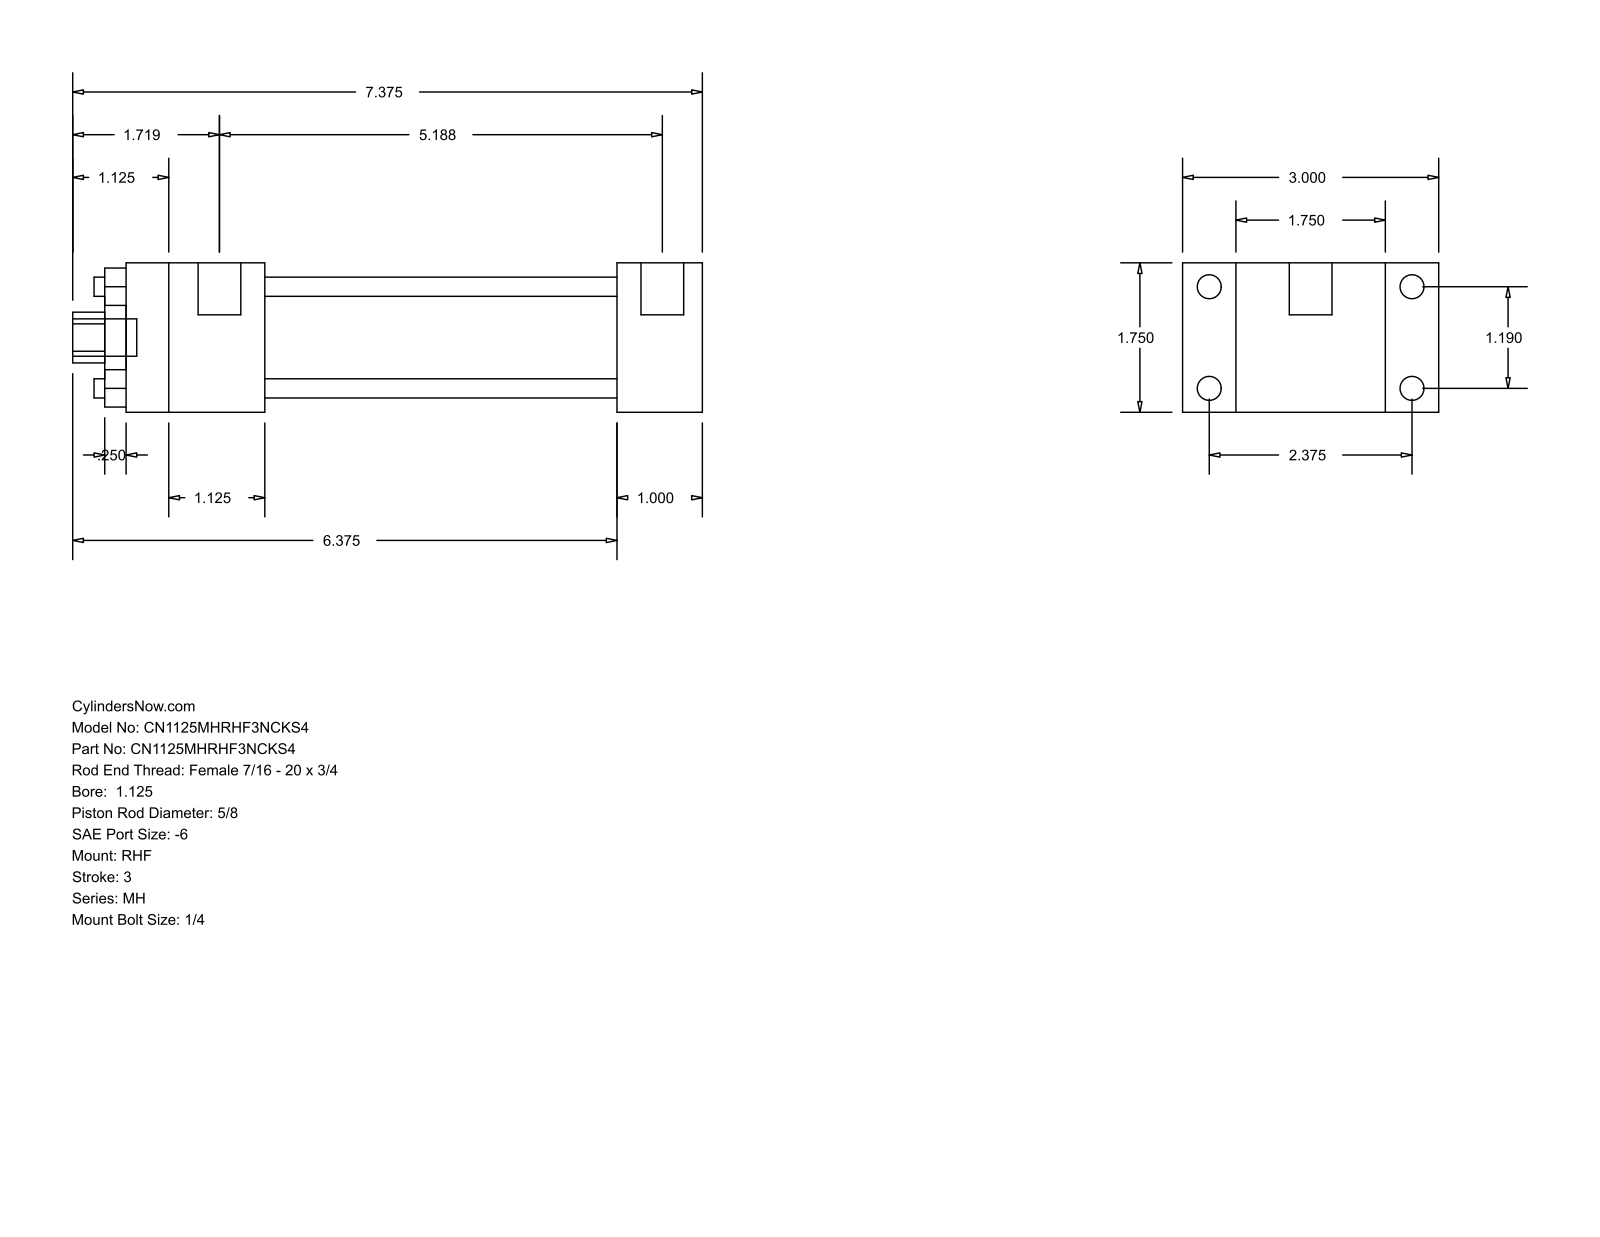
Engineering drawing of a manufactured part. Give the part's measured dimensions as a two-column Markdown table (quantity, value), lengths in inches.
| quantity | value |
| --- | --- |
| part name | MH_RHF__0112_0.625 |
| STEP written by | GSSL Pune (CONFIG_CONTROL_DESIGN) |
| units | inches |
| bodies | 0 solids, 88 faces (60 planar, 28 cylindrical, 0 other) |
| overall size | 7.375 × 3 × 1.75 |
| round holes (diameter × count) | 0.225 × 4, 0.625 × 1, 1.125 × 1, 1.375 × 1 |
| round bosses / shafts (diameter × count) | 0.281 × 4, 0.219 × 4, 0.5 × 2, 0.437 × 1 |
| partial cylindrical surfaces (radius × count) | 0.297 × 1 |
| main face-to-face distances | 1.75, 0.625, 2.375, 1, 3, 4.125, 5.125, 1.625, 5.75, 6.75 |
| hole center spacings | 0.841, 1.19, 1.683 |
